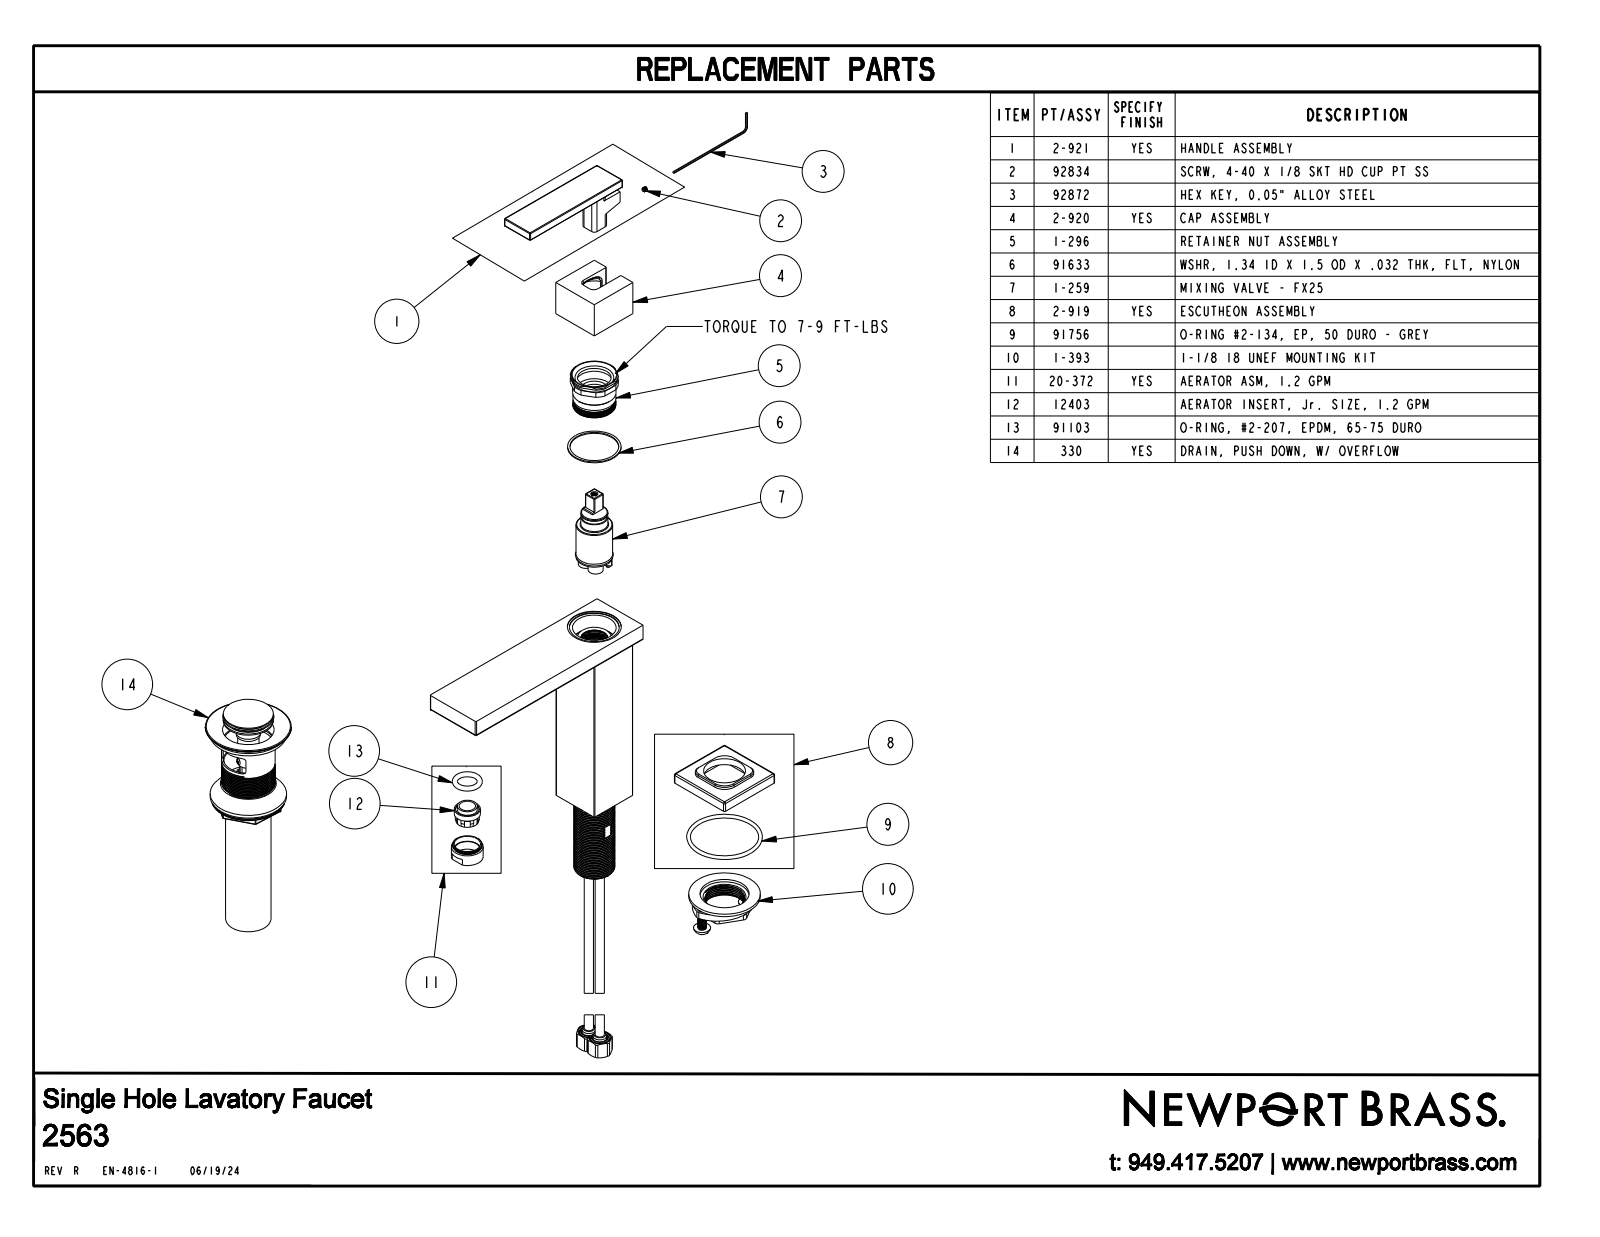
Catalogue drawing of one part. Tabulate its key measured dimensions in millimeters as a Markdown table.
| quantity | value |
| --- | --- |
| part name | 2563_SW0001 |
| STEP written by | CREO PARAMETRIC BY PTC INC, 2018400 (AUTOMOTIVE_DESIGN) |
| units | millimeters |
| bodies | 2 solids, 108 faces (45 planar, 45 cylindrical, 18 other) |
| overall size | 193.9 × 166.1 × 50 |
| volume | 361 500 mm³ |
| surface area | 59 900 mm² |
| round bosses / shafts (diameter × count) | 22.2 × 1 |
| partial cylindrical surfaces (radius × count) | 0.5 × 21, 0.8 × 8, 1 × 8, 3.2 × 4, 2.5 × 2 |
| main face-to-face distances | 38.1, 12.7, 3.7, 41.8, 6.4, 139.2, 151.9, 193.9, 54.7, 42 |
